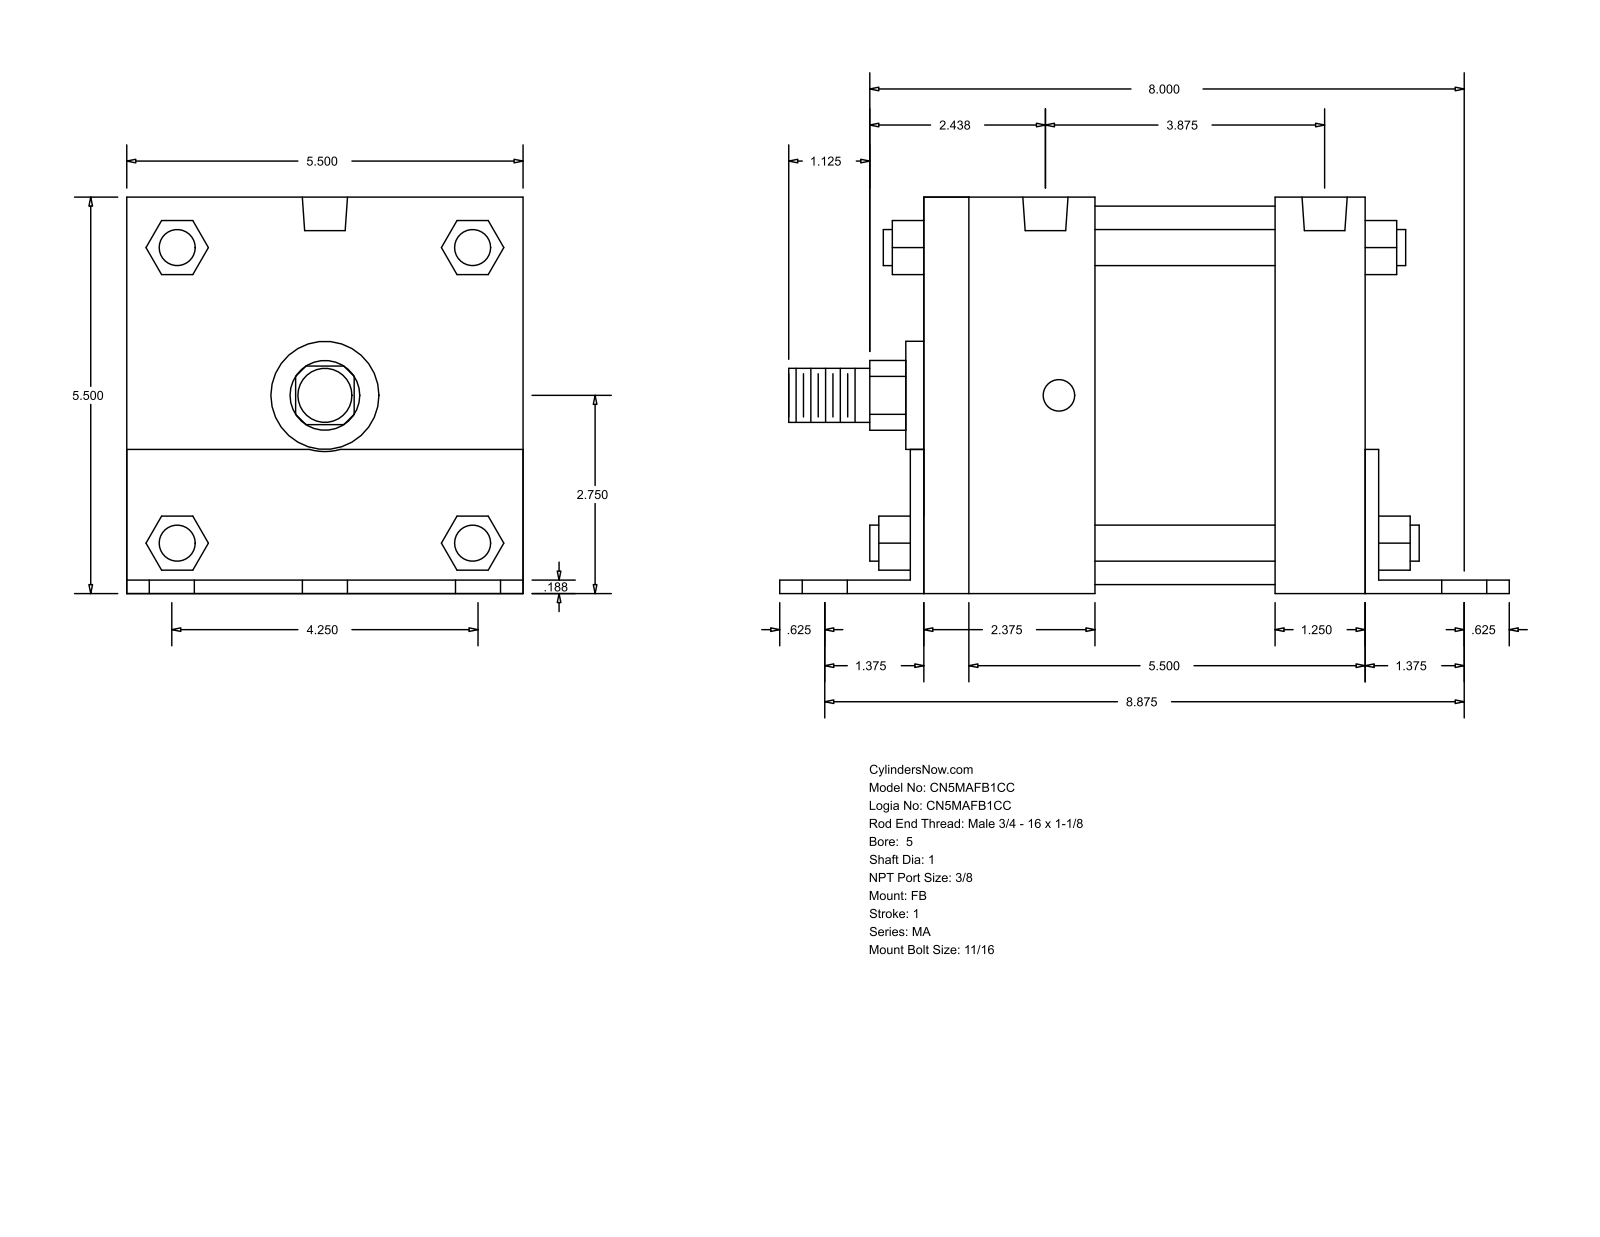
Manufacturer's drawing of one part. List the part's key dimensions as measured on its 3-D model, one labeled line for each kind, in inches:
Part name (STEP PRODUCT): MA_FB__0500_1
STEP written by: GSSL Pune (CONFIG_CONTROL_DESIGN)
Units: inches
Bodies: 0 solids, 140 faces (105 planar, 35 cylindrical, 0 other)
Overall size (bounding box): 10.125 × 5.502 × 5.5
Round holes (diameter × count): ⌀0.687 ×6, ⌀0.437 ×4, ⌀0.627 ×2
Round bosses / shafts (diameter × count): ⌀0.5 ×4, ⌀5.25 ×1, ⌀1.5 ×1, ⌀1 ×1, ⌀0.75 ×1
Partial cylindrical surfaces — rounded edges, fillets, slot ends (radius × count): R0.484 ×1, R0.78 ×1
Main face-to-face distances: 5.5, 0.187, 5.502, 0.185, 5.315, 6.125, 0.188, 6.313, 6.312, 6.5
Hole centre spacings: 2.125, 9.126, 8.875, 2.876, 3.006, 3.5, 3.728, 3.883
